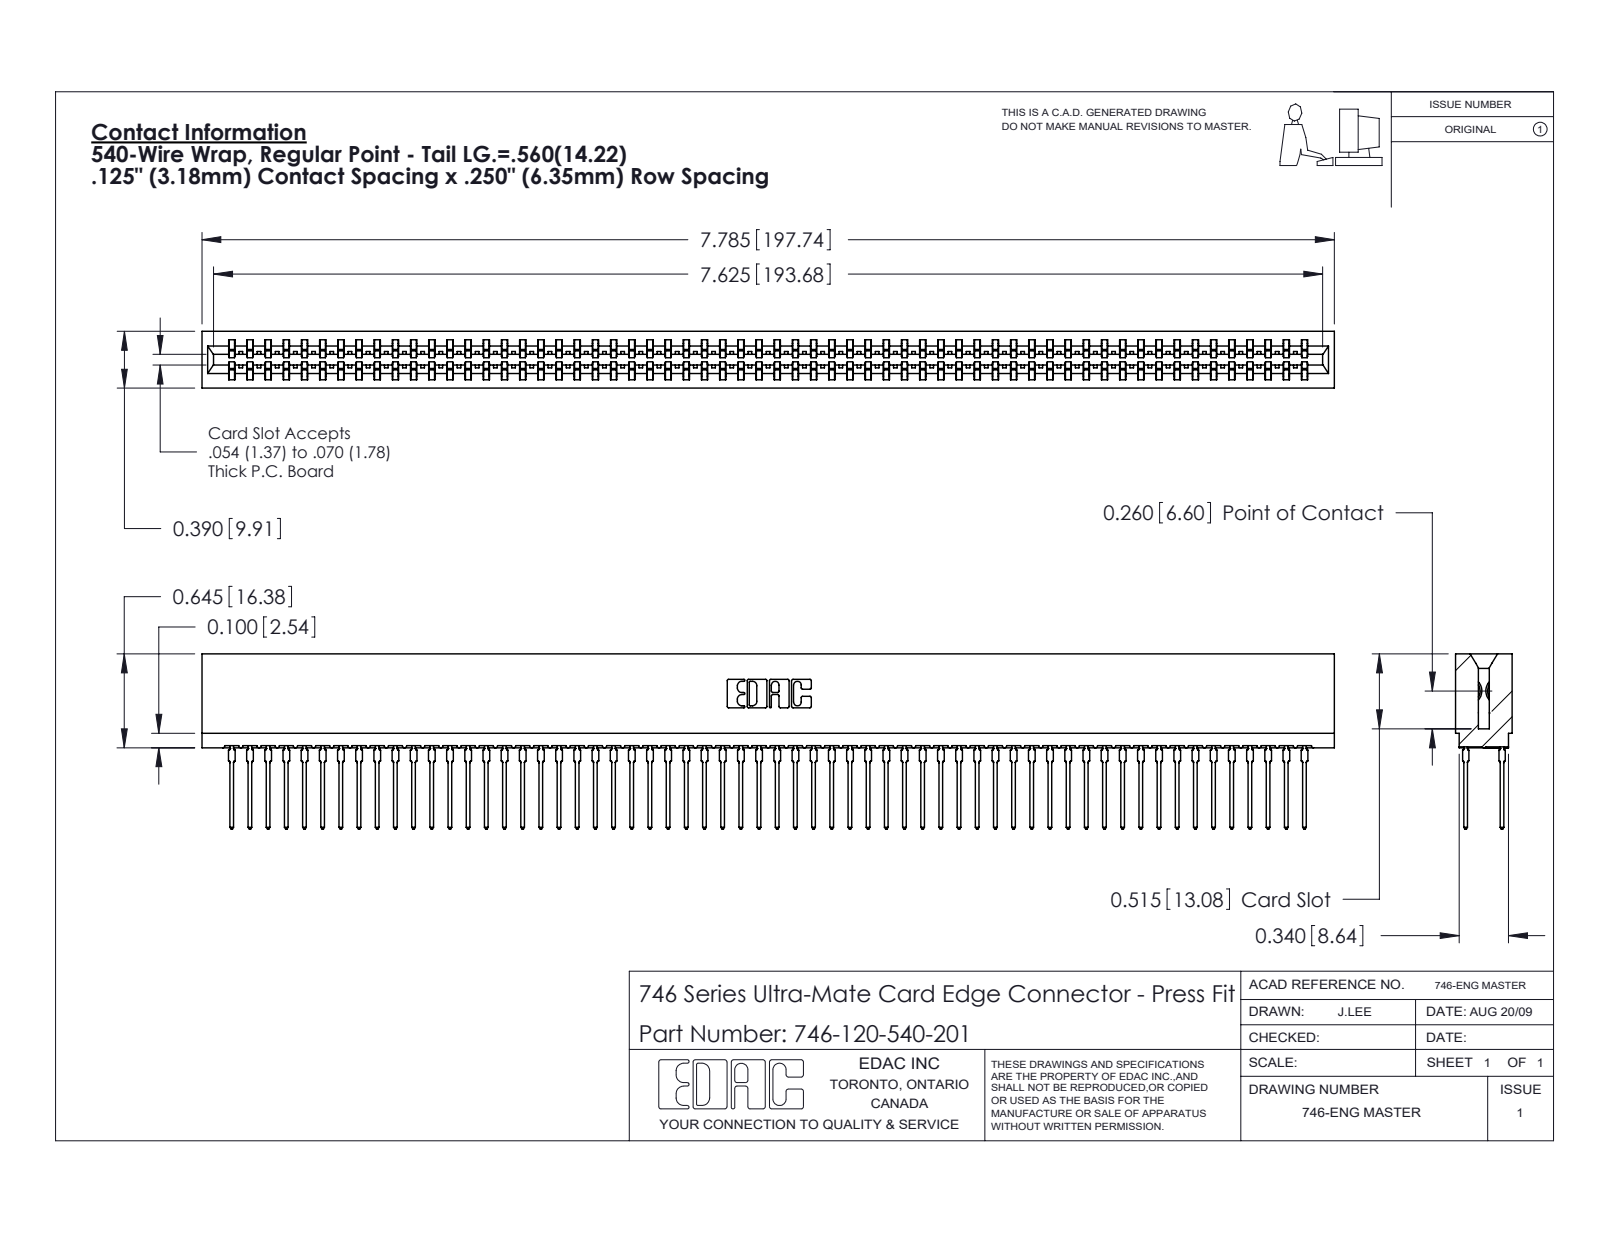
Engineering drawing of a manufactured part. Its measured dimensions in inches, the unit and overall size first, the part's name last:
Units: inches
Overall size (bounding box): 7.785 × 1.204 × 0.39
Partial cylindrical surfaces — rounded edges, fillets, slot ends (radius × count): R0.021 ×240, R0.015 ×61, R0.01 ×22, R0.005 ×8, R0.011 ×8, R0.007 ×6, R0.031 ×6, R0.026 ×3
Main face-to-face distances: 0.057, 0.333, 0.39, 0.025, 0.25, 0.307, 0.275, 0.083, 0.174, 0.158
Volume: 1.309 in³ · Surface area: 56.54 in²
Bodies: 121 solids, 10837 faces (5575 planar, 2142 cylindrical, 3120 other)
Part name (STEP PRODUCT): 746-292-001_540; 746 Part_.515 Slot Depth - 01; 746-120-540-201
STEP written by: SolidWorks 2020 (CONFIG_CONTROL_DESIGN)
